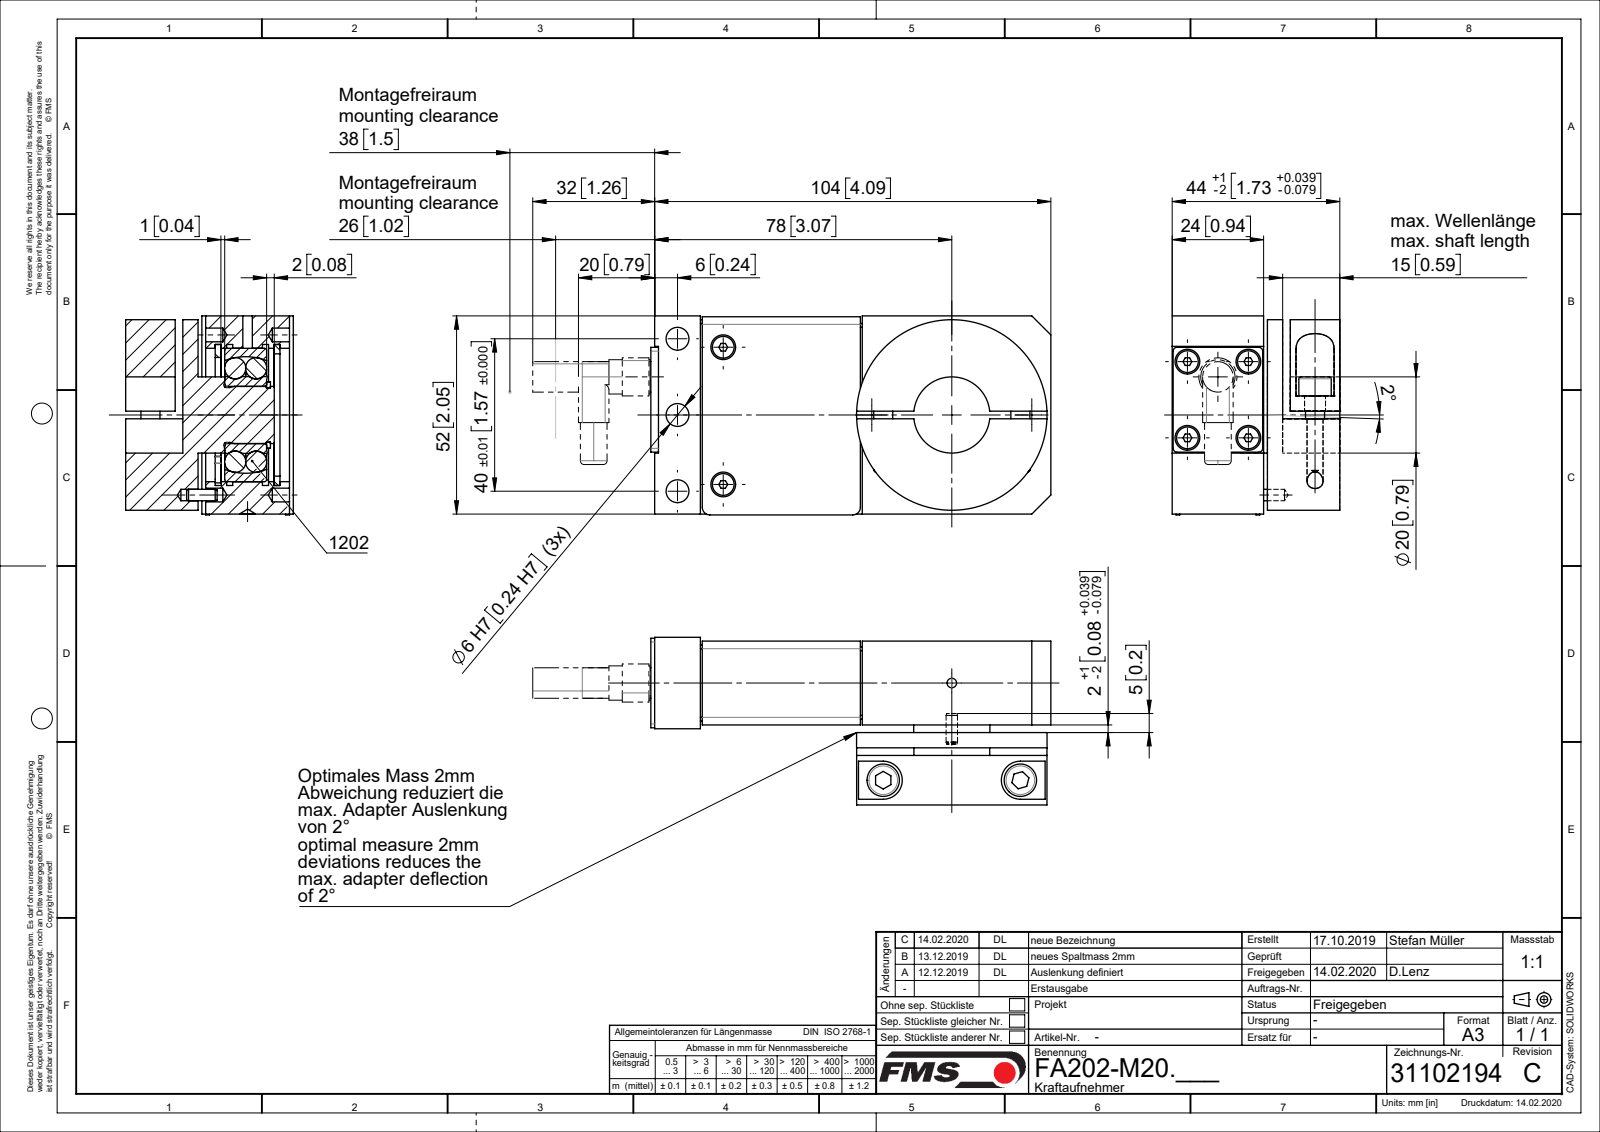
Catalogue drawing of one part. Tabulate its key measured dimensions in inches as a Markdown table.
| quantity | value |
| --- | --- |
| part name | F0807306C_DM20; F0807304; F0807305; SENKSCHRAUBE_I-6KT_M3X6 (+8 more) |
| STEP written by | Mechanical Desktop 2009 (CONFIG_CONTROL_DESIGN) |
| units | inches |
| bodies | 26 solids, 606 faces (229 planar, 221 cylindrical, 156 other) |
| overall size | 4.843 × 2.047 × 1.969 |
| volume | 8.476 in³ |
| surface area | 91.74 in² |
| round holes (diameter × count) | 0.102 × 7, 0.039 × 4, 0.126 × 4, 0.142 × 4, 0.236 × 4, 0.17 × 2, 0.217 × 2, 0.118 × 1, 0.157 × 1, 0.256 × 1, 0.276 × 1, 0.563 × 1 |
| round bosses / shafts (diameter × count) | 0.236 × 7, 0.118 × 6, 0.039 × 4, 0.315 × 3, 0.394 × 2, 0.197 × 2, 1.969 × 1, 0.89 × 1 |
| partial cylindrical surfaces (radius × count) | 0.079 × 8, 0.039 × 6, 0.197 × 2, 0.161 × 1 |
| main face-to-face distances | 0.039, 0.827, 0.866, 0.059, 0.079, 0.236, 0.098, 0.748, 0.709, 0.768 |
| hole center spacings | 0.088, 0.787, 0.827, 1.169, 0.079, 0.394, 0.142, 0.284 |
